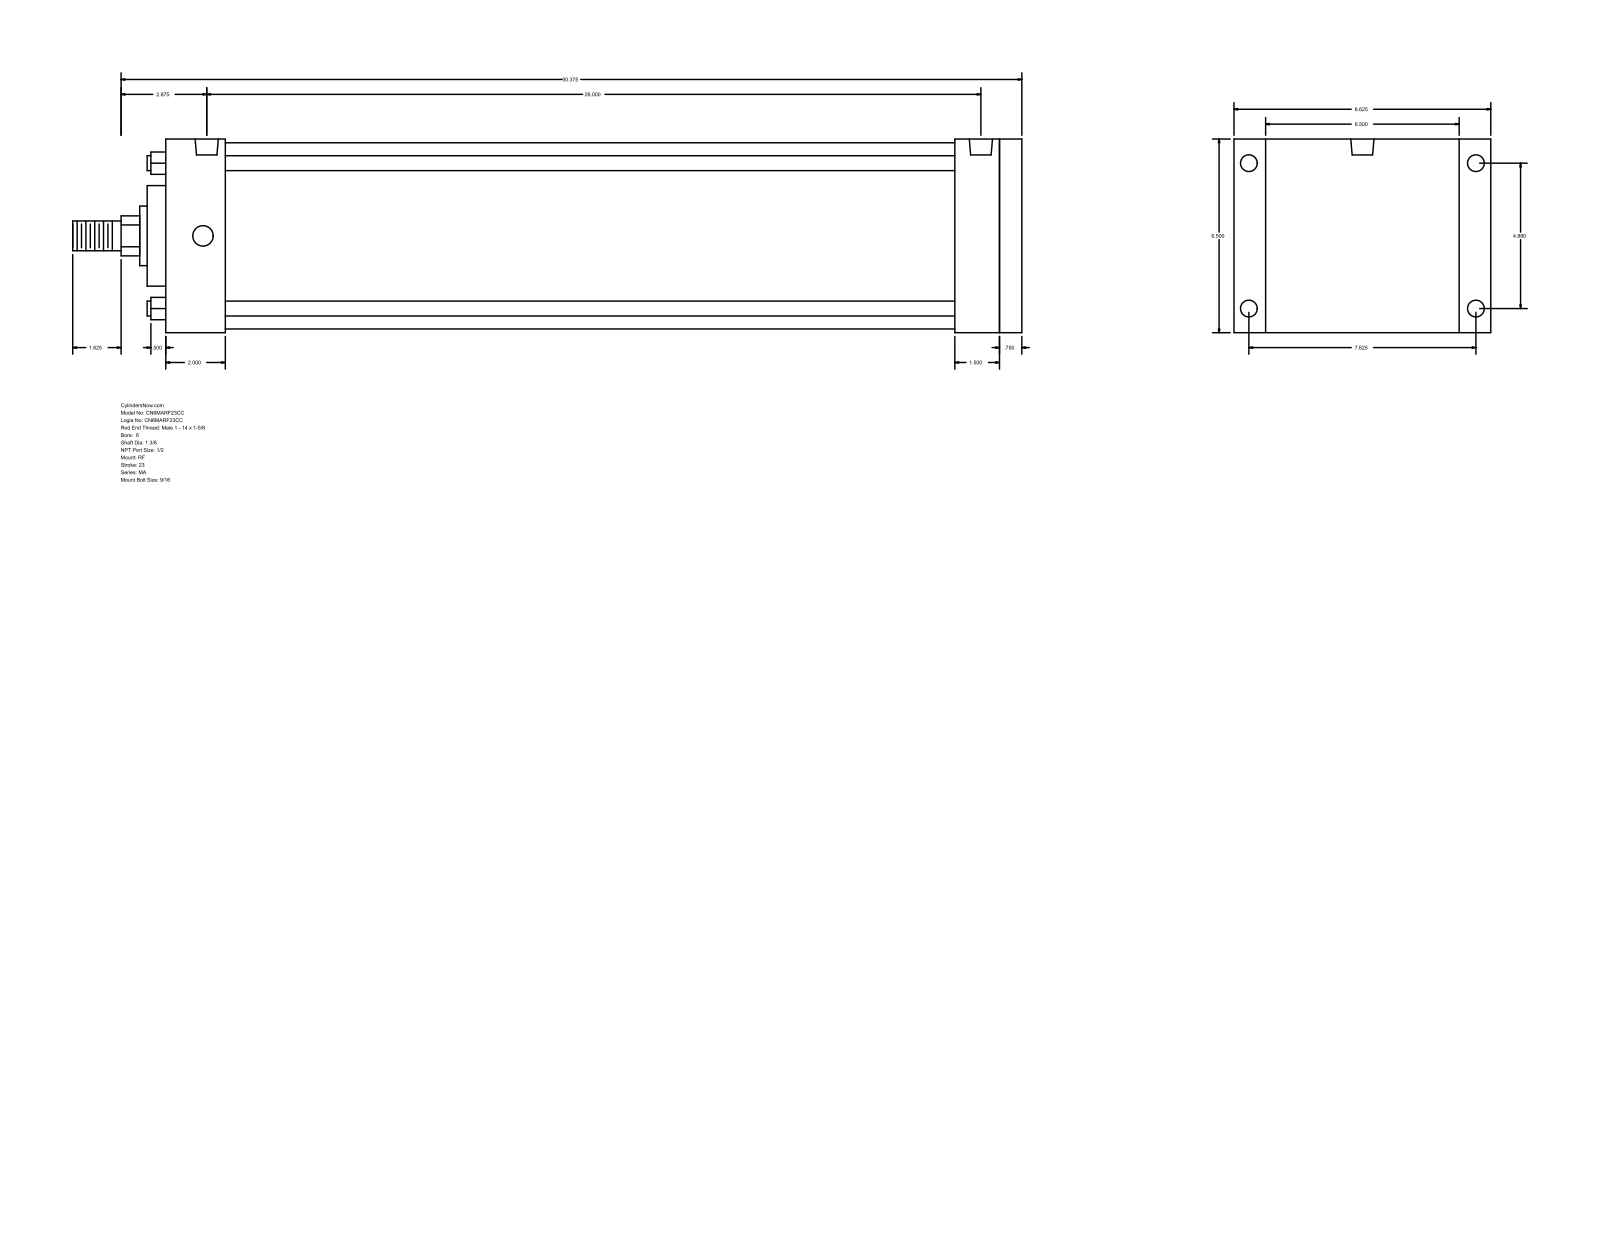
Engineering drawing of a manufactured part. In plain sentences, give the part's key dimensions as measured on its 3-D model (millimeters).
The part is named "MA_RF__0600_1.375". Its 3-D file was written by "GSSL Pune (CONFIG_CONTROL_DESIGN)". It is 0 solids with 94 faces: 65 planar, 29 cylindrical and 0 other. Overall it measures 812.8 by 219.07 by 165.1 millimeters. Round holes: 4 of diameter 14.29, 4 of diameter 17.46, 2 of diameter 19.77. Round bosses or shafts: 4 of diameter 12.7, 1 of diameter 158.75, 1 of diameter 85.72, 1 of diameter 50.8, 1 of diameter 34.92, 1 of diameter 25.4. Partial cylindrical surfaces (rounded edges, fillets, slot ends): 1 of radius 17.06. The main face-to-face distances are 165.1, 733.42, 714.38, 19.04, 38.1, 50.8, 663.58, 682.62, 676.28, 625.48. The hole center spacings are 123.96, 193.68, 229.95, 663.57, 3.18, 660.39.
